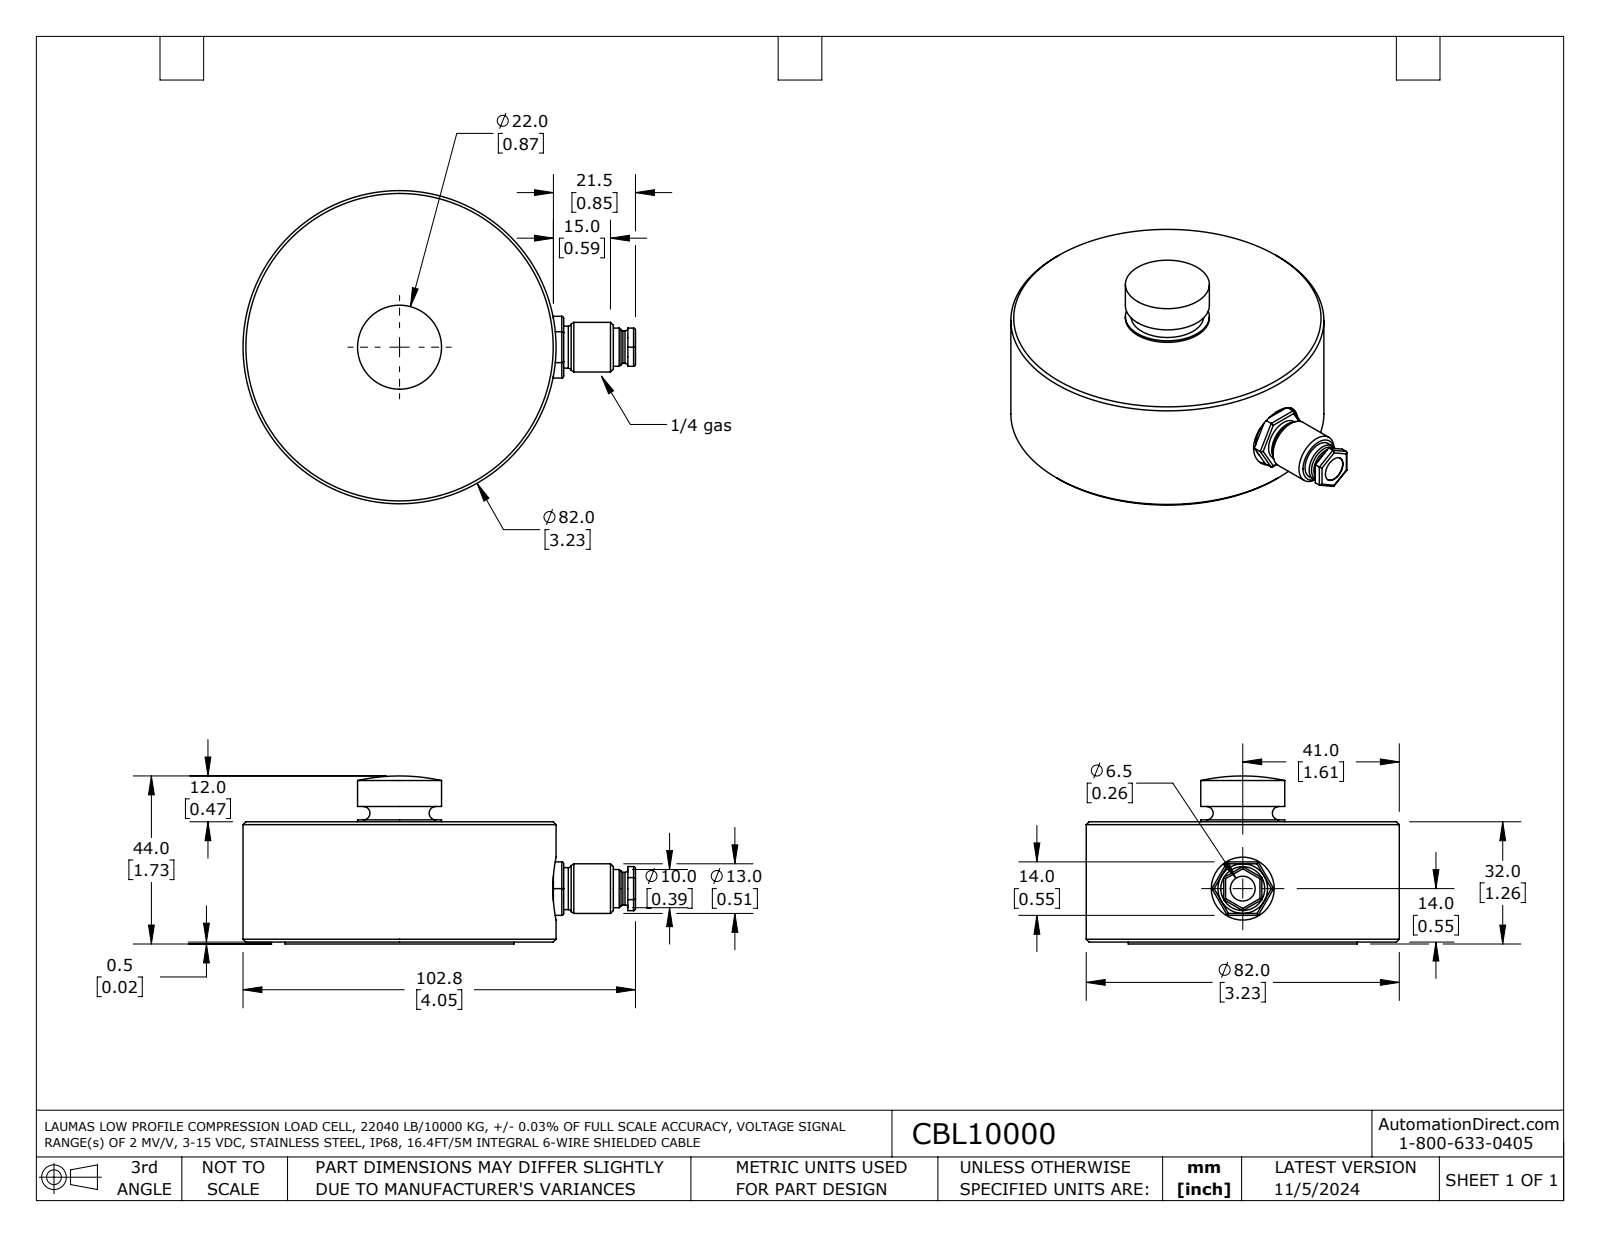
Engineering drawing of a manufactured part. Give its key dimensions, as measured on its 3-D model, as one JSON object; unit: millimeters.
{"part_name": "CBL10000", "step_written_by": "SolidWorks 2021 (AUTOMOTIVE_DESIGN)", "units": "millimeters", "bodies": {"solids": 2, "faces": 86, "planar": 31, "cylindrical": 36, "other": 19}, "overall_size": [102.8, 82, 44], "volume_mm3": 170800, "surface_area_mm2": 21060, "round_holes": [[6.5, 1], [16.5, 1], [54.6, 1]], "round_bosses_or_shafts": [[82, 1], [60, 1], [22, 1], [13.5, 1], [13, 1], [11, 1], [10, 1], [8.5, 1]], "partial_cylinders_radius": [[0.5, 12]], "face_to_face_distances": [30.8, 0.8, 31.5, 0.5, 32, 1.2, 3.5, 32.5, 31.2, 36]}
